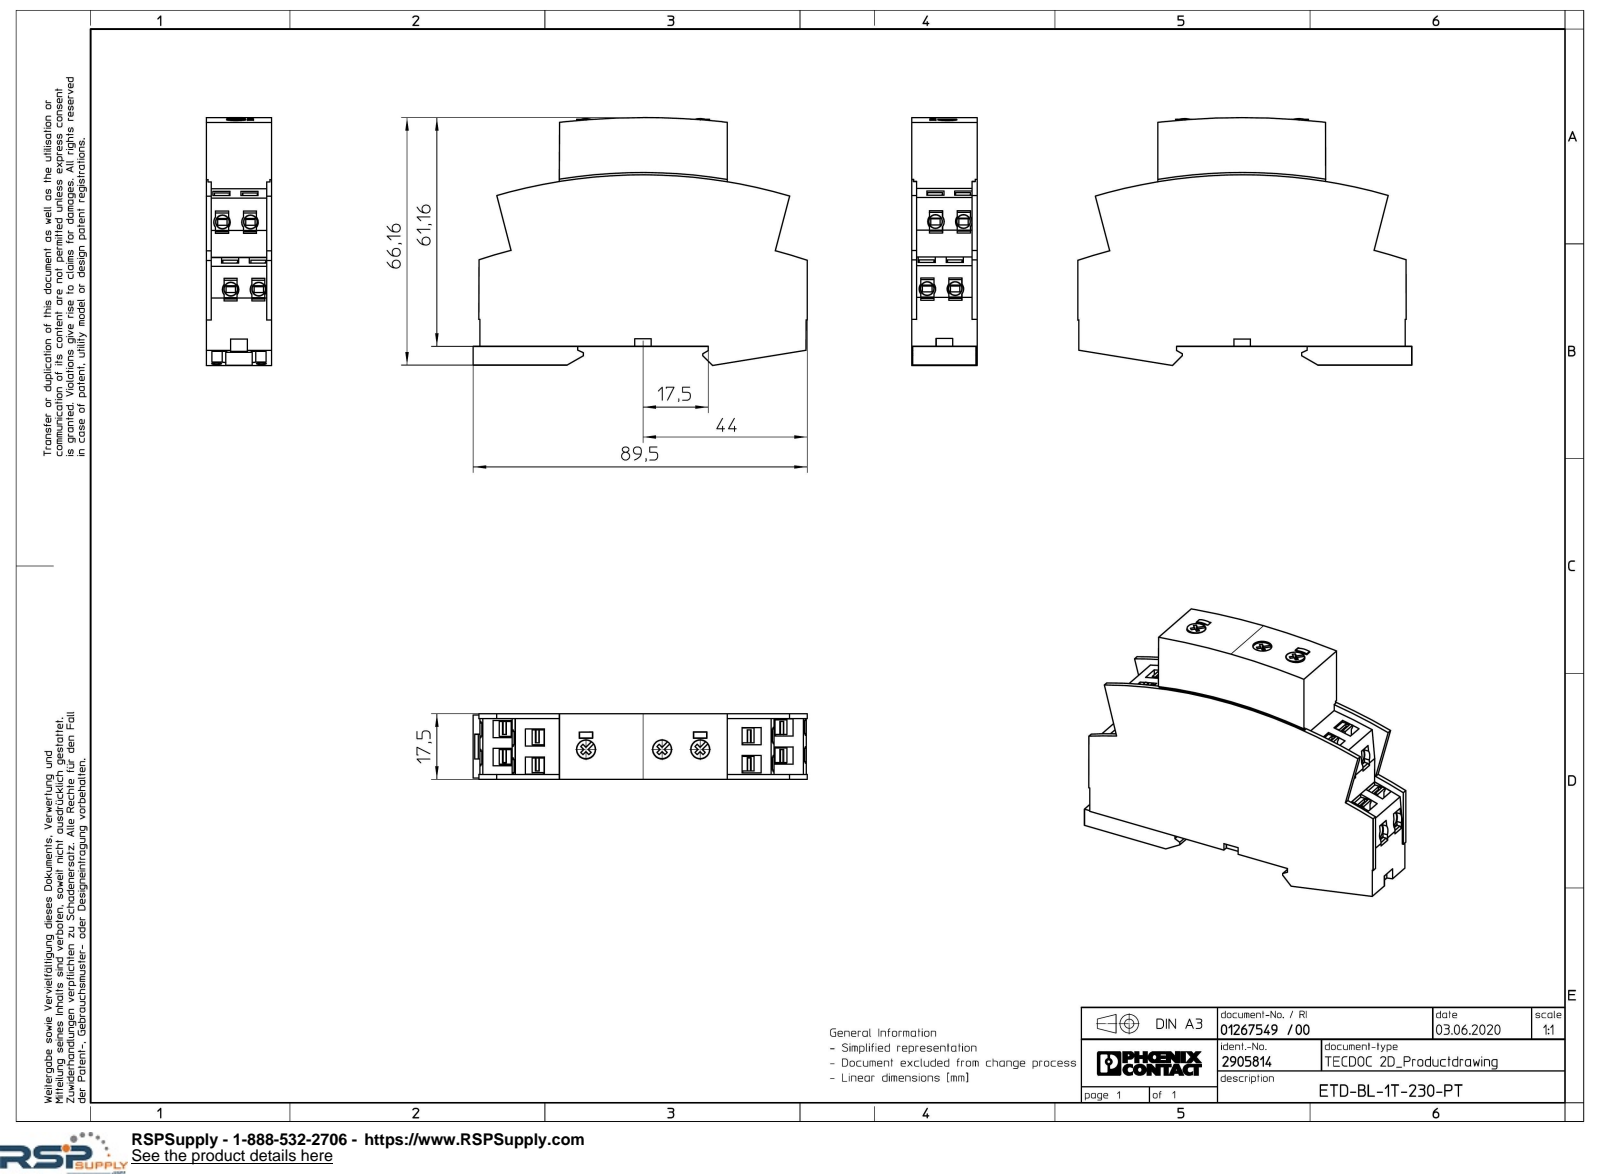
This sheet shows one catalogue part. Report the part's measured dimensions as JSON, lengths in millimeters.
{"part_name": "ETD-BL-1T-230-PT-select", "step_written_by": "Creo Elements/Direct Modeling 20.1A 29-Sep-2018 (C) Parametric Technology GmbH (AUTOMOTIVE_DESIGN)", "units": "millimeters", "bodies": {"solids": 1, "faces": 588, "planar": 460, "cylindrical": 92, "other": 36}, "overall_size": [89.5, 66.27, 17.5], "volume_mm3": 74514, "surface_area_mm2": 17497, "round_holes": [[2.5, 3], [5.1, 3], [2.6, 2]], "round_bosses_or_shafts": [[5, 3]], "partial_cylinders_radius": [[0.3, 9], [0.5, 9], [2.2, 8], [0.8, 4], [140, 3], [0.4, 2], [6.25, 2], [138.2, 2]], "face_to_face_distances": [17.5, 5, 1.3, 1, 16.2, 15.9, 17.2, 87.4, 17.95, 14.9], "hole_center_spacings": [5, 3.37, 4.19, 8.59, 8.77, 10, 10.2, 12]}
